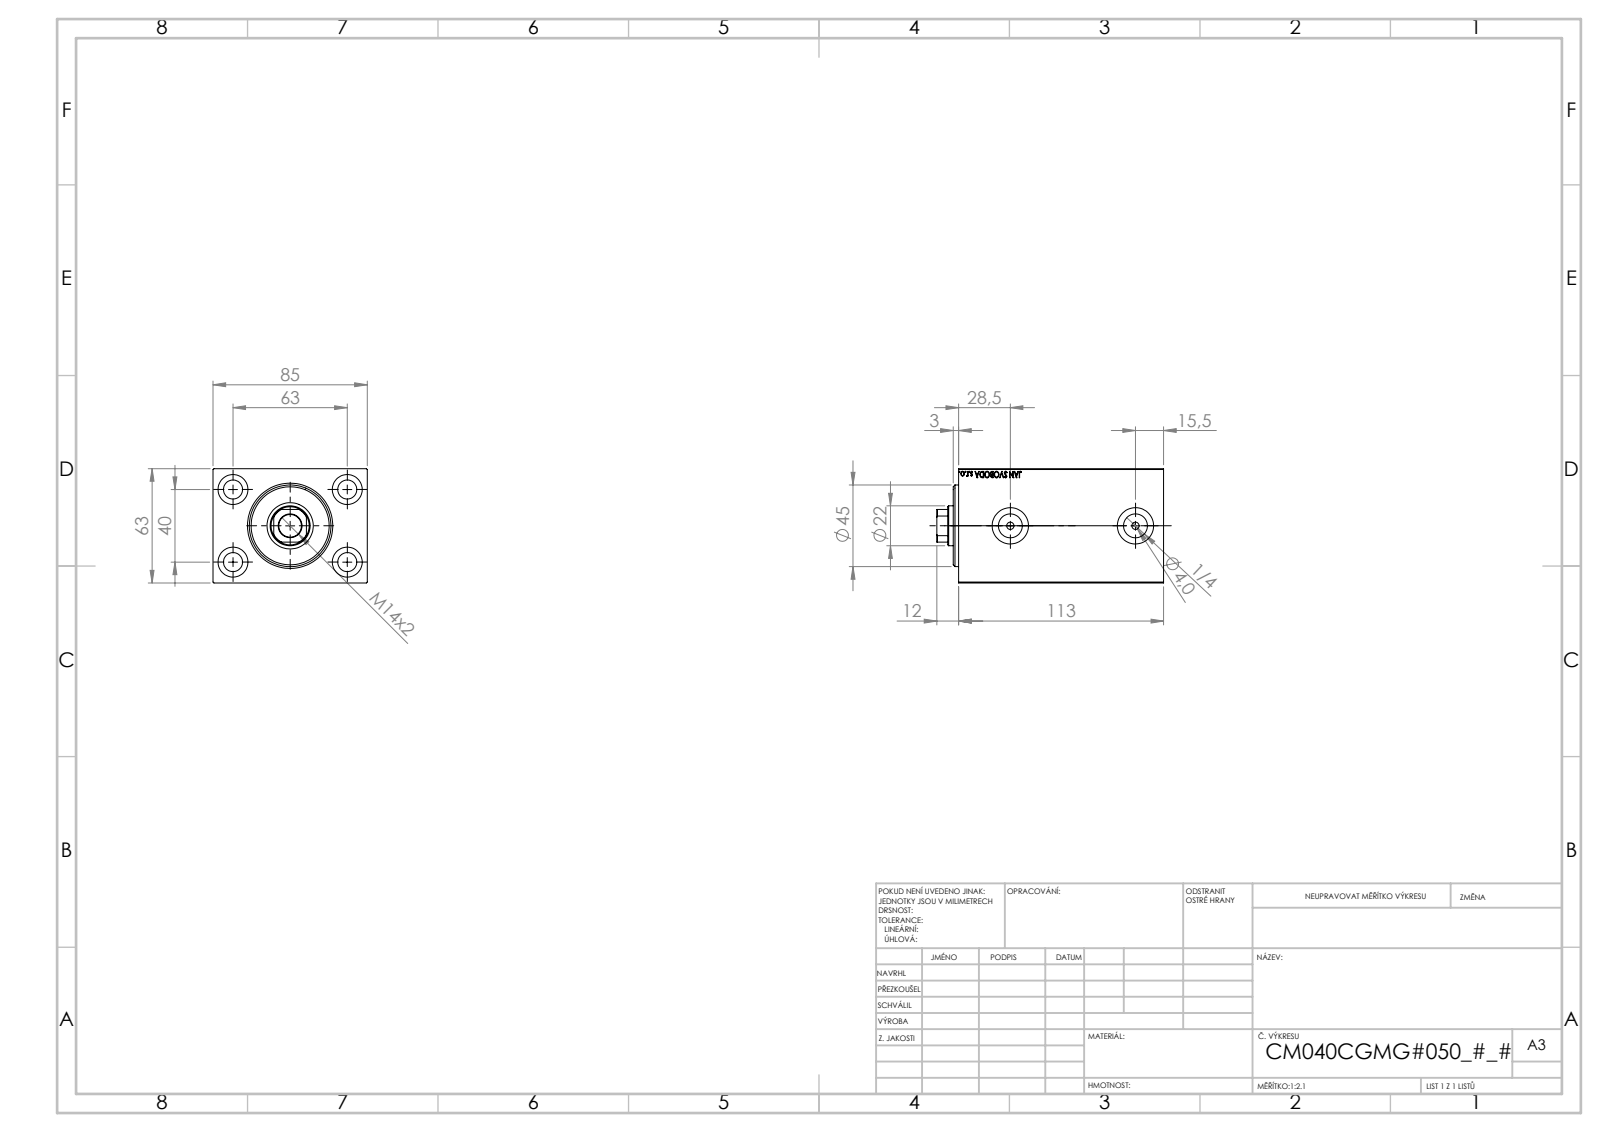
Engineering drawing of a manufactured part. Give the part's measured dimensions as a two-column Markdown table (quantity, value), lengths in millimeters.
| quantity | value |
| --- | --- |
| part name | V450CM_C_VCP; V450CM_C_Body; V450CM_VC_B |
| STEP written by | SolidWorks 2019 (CONFIG_CONTROL_DESIGN) |
| units | millimeters |
| bodies | 3 solids, 862 faces (408 planar, 60 cylindrical, 394 other) |
| overall size | 125 × 85 × 63 |
| volume | 511 899 mm³ |
| surface area | 95 238 mm² |
| round holes (diameter × count) | 10.5 × 4, 16.5 × 4, 4 × 2, 13.16 × 2, 20 × 2, 12.5 × 1, 22 × 1, 25.5 × 1, 40 × 1, 42 × 1, 45 × 1 |
| partial cylindrical surfaces (radius × count) | 10.5 × 1 |
| main face-to-face distances | 63, 85, 113, 12, 101, 28.6, 72.4, 84.4, 11, 102 |
| hole center spacings | 37.31, 40, 63, 74.63, 69 |
